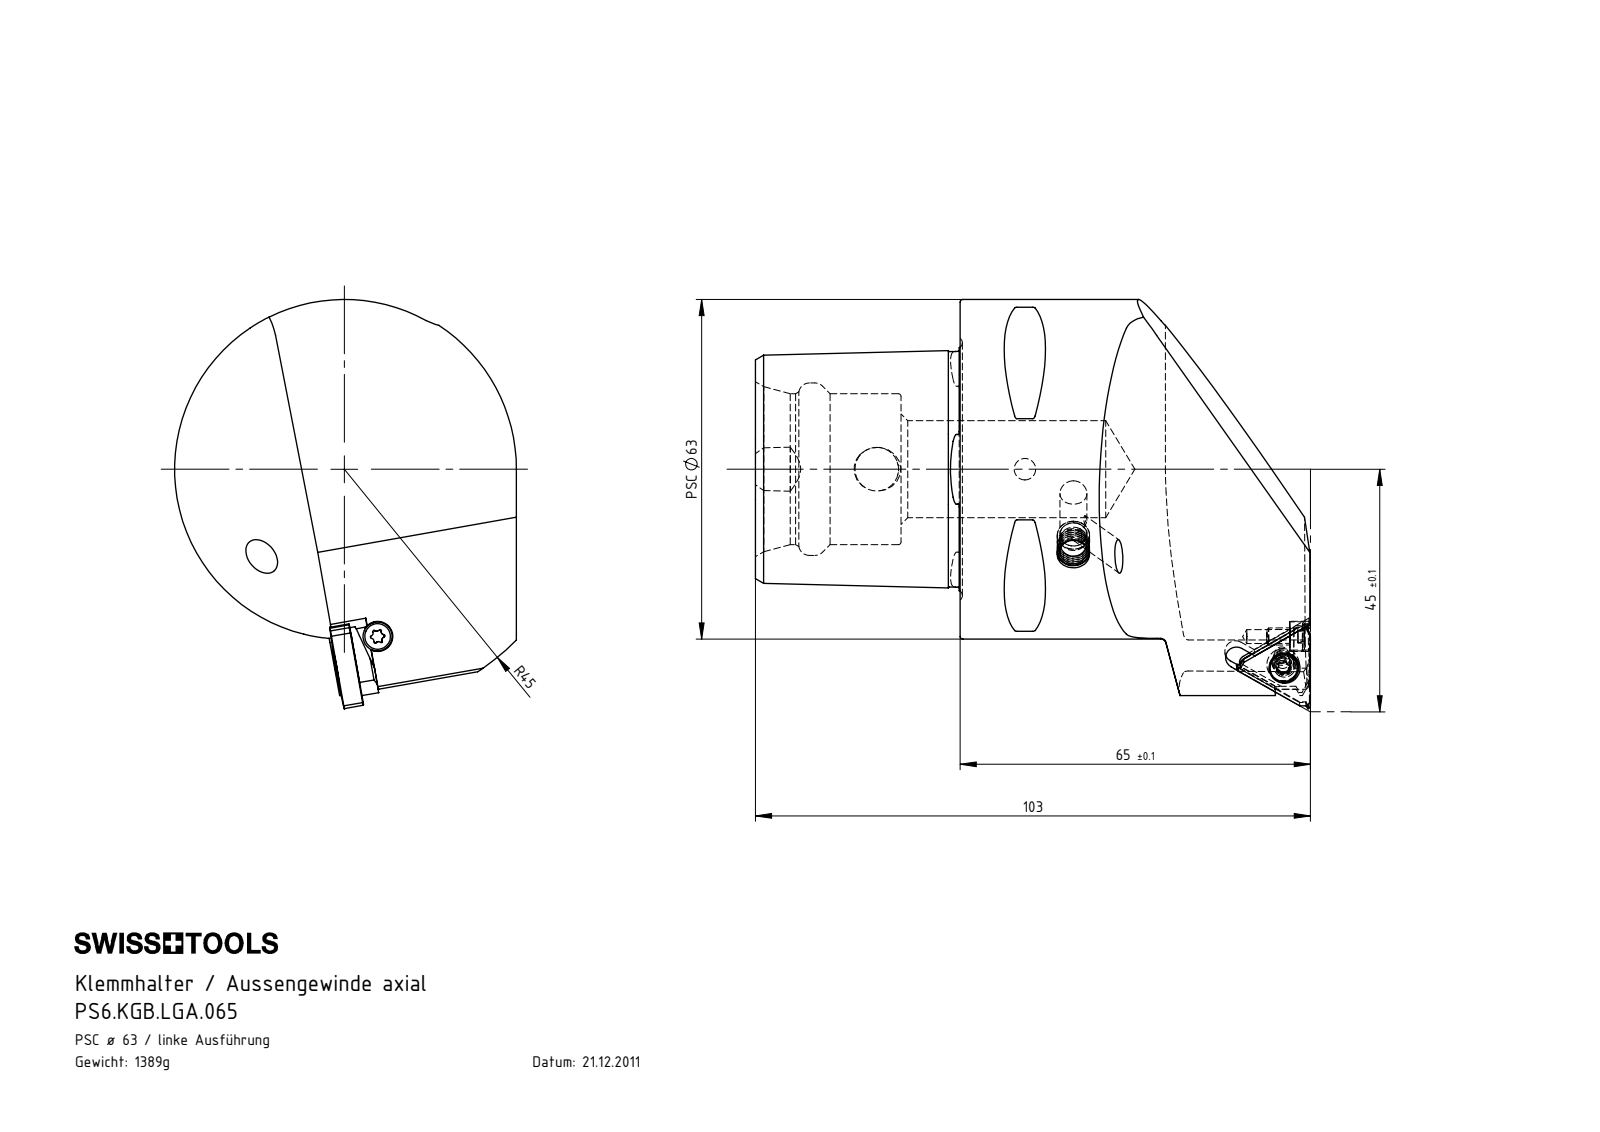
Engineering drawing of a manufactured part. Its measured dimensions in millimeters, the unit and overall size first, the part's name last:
Units: millimetres
Overall size (bounding box): 103 × 75.91 × 63.46
Round holes (diameter × count): ⌀2.58 ×2, ⌀4 ×2, ⌀5 ×2, ⌀4.02 ×1, ⌀8.1 ×1, ⌀18 ×1, ⌀28 ×1, ⌀32 ×1
Round bosses / shafts (diameter × count): ⌀3.18 ×2, ⌀63 ×1, ⌀6 ×1, ⌀5.5 ×1, ⌀5.4 ×1, ⌀2.78 ×1
Partial cylindrical surfaces — rounded edges, fillets, slot ends (radius × count): R0.23 ×12, R0.57 ×12, R0.5 ×8, R0.1 ×2, R6 ×2, R0.25 ×1, R1.3 ×1, R1.75 ×1
Main face-to-face distances: 38, 24.88, 11, 27, 3.45, 55.8, 3.2, 6.65, 37.8, 10.8
Hole centre spacings: 27.5, 467.55, 467.6
Volume: 174 242 mm³ · Surface area: 29 312 mm²
Bodies: 7 solids, 309 faces (88 planar, 95 cylindrical, 126 other)
Part name (STEP PRODUCT): PS6-KGB.LGA.065; WGB-ER2.001.012_A; LT16ER; WGB-ER3.001.007_A (+3 more)
STEP written by: SolidWorks 2012 (CONFIG_CONTROL_DESIGN)
